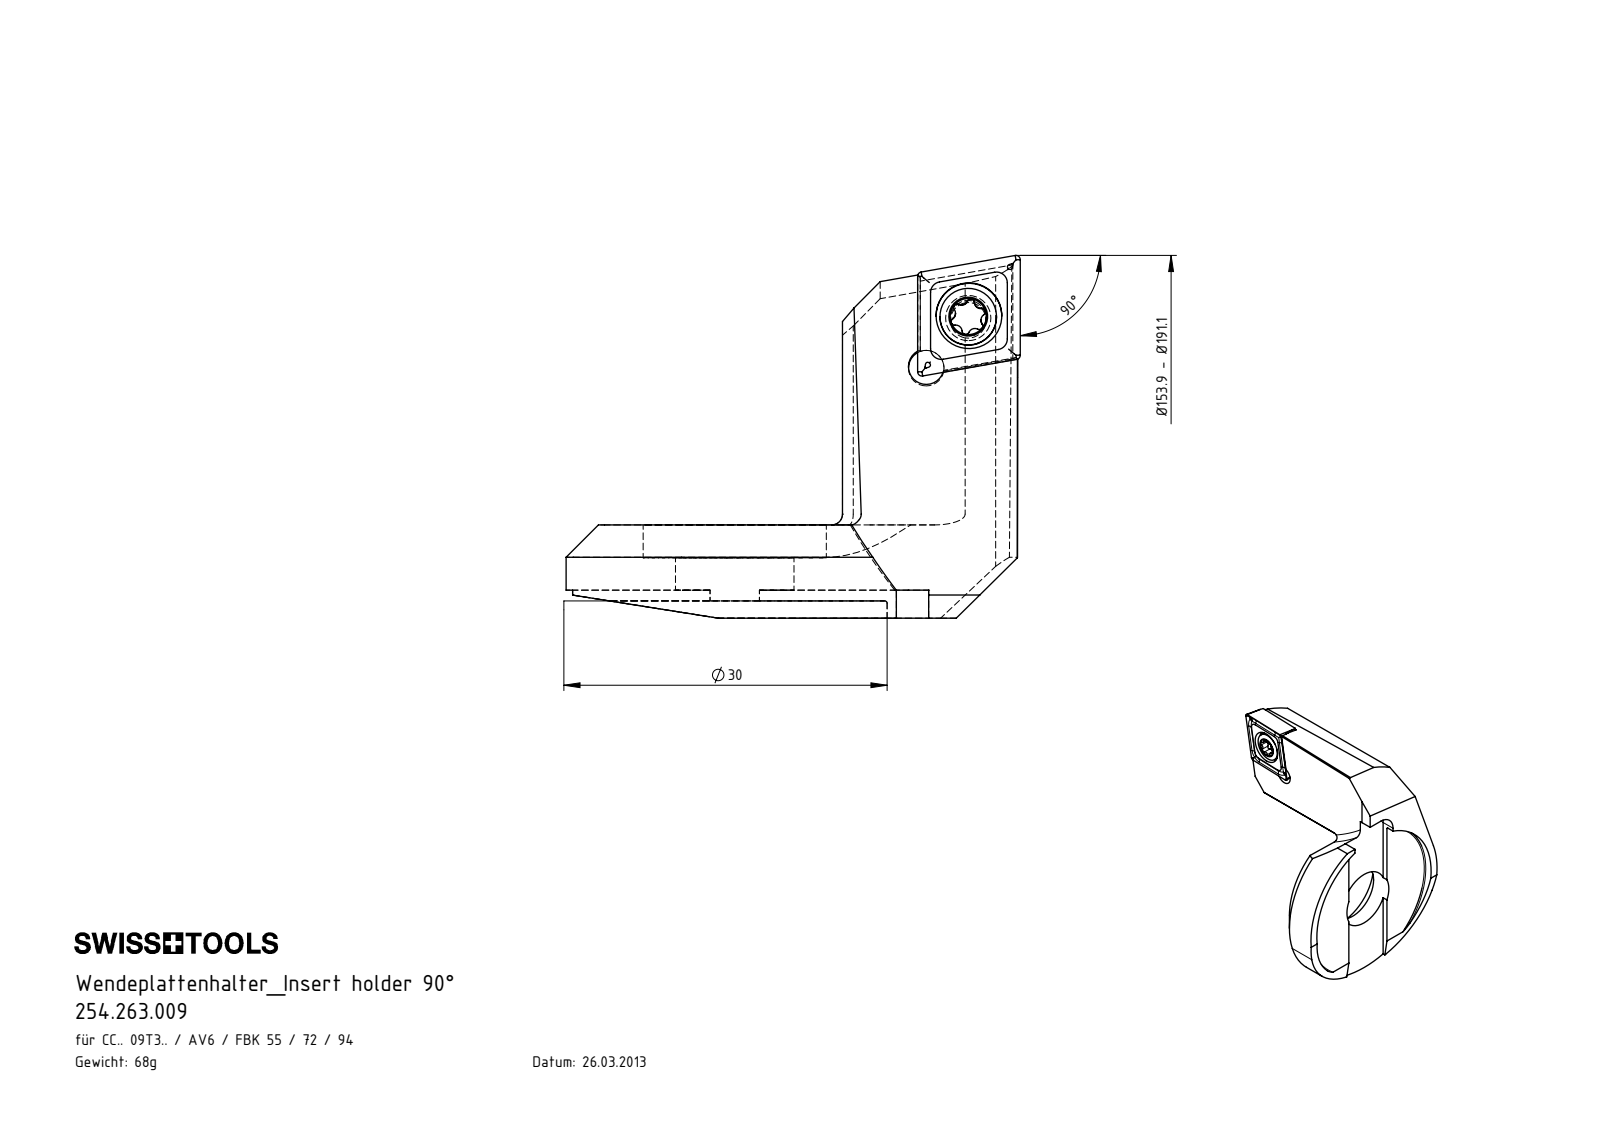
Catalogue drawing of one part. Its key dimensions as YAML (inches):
part_name: "WCB-ER2.001.009_A; AV6.WCB.001.032; CCMT09T304; AV6-WCB.001.032_A_fertigbearbeitet"
step_written_by: "SolidWorks 2017 (AUTOMOTIVE_DESIGN)"
units: inches
bodies: {solids: 3, faces: 136, planar: 53, cylindrical: 36, other: 47}
overall_size: [1.659, 1.325, 1.303]
volume: 0.529
surface_area: 7.009
round_holes:
  - {diameter: 0.13, count: 2}
  - {diameter: 0.173, count: 1}
  - {diameter: 0.24, count: 1}
  - {diameter: 0.433, count: 1}
  - {diameter: 0.669, count: 1}
round_bosses_or_shafts:
  - {diameter: 0.207, count: 1}
  - {diameter: 0.157, count: 1}
partial_cylinders:
  - {radius: 0.013, count: 6}
  - {radius: 0.023, count: 6}
  - {radius: 0.039, count: 4}
  - {radius: 0.591, count: 3}
  - {radius: 0.126, count: 2}
  - {radius: 0.652, count: 1}
  - {radius: 0.825, count: 1}
  - {radius: 1.969, count: 1}
face_to_face_distances: [0.278, 0.039, 0.238, 0.157, 0.118, 0.12, 0.341, 0.22, 0.102, 0.063]
hole_center_spacings: [0.239, 0.243]
